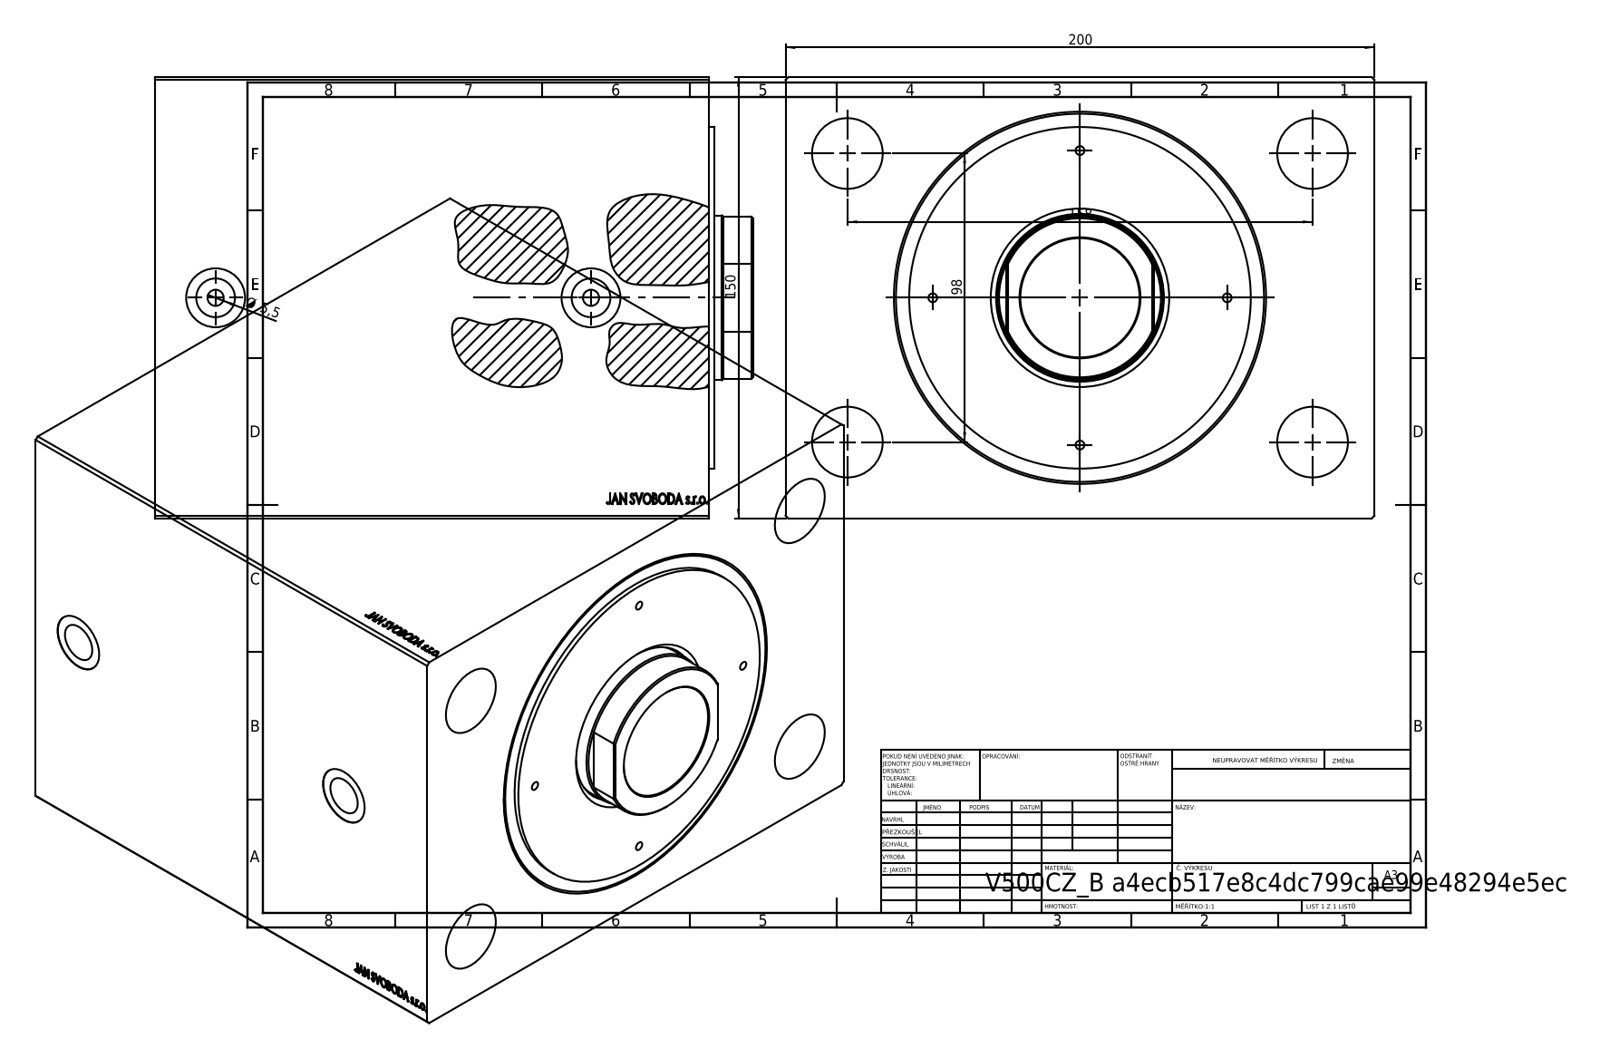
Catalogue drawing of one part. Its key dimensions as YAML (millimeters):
part_name: "V500CZ_B_VC; V500CZ"
step_written_by: "SolidWorks 2019 (CONFIG_CONTROL_DESIGN)"
units: millimeters
bodies: {solids: 3, faces: 874, planar: 400, cylindrical: 58, other: 416}
overall_size: [203, 200, 150]
volume: 5681000
surface_area: 426388
round_holes:
  - {diameter: 3, count: 4}
  - {diameter: 24, count: 4}
  - {diameter: 5.5, count: 2}
  - {diameter: 13.16, count: 2}
  - {diameter: 20, count: 2}
  - {diameter: 36, count: 1}
  - {diameter: 40.5, count: 1}
  - {diameter: 56, count: 1}
  - {diameter: 57, count: 1}
  - {diameter: 100, count: 1}
  - {diameter: 125, count: 1}
round_bosses_or_shafts:
  - {diameter: 116, count: 1}
partial_cylinders:
  - {radius: 27.5, count: 1}
face_to_face_distances: [150, 200, 34, 50, 188, 154, 138, 16, 1.8, 139.8]
hole_center_spacings: [50, 56.94, 70.71, 79.01, 92.96, 126.66, 137.99, 98]
